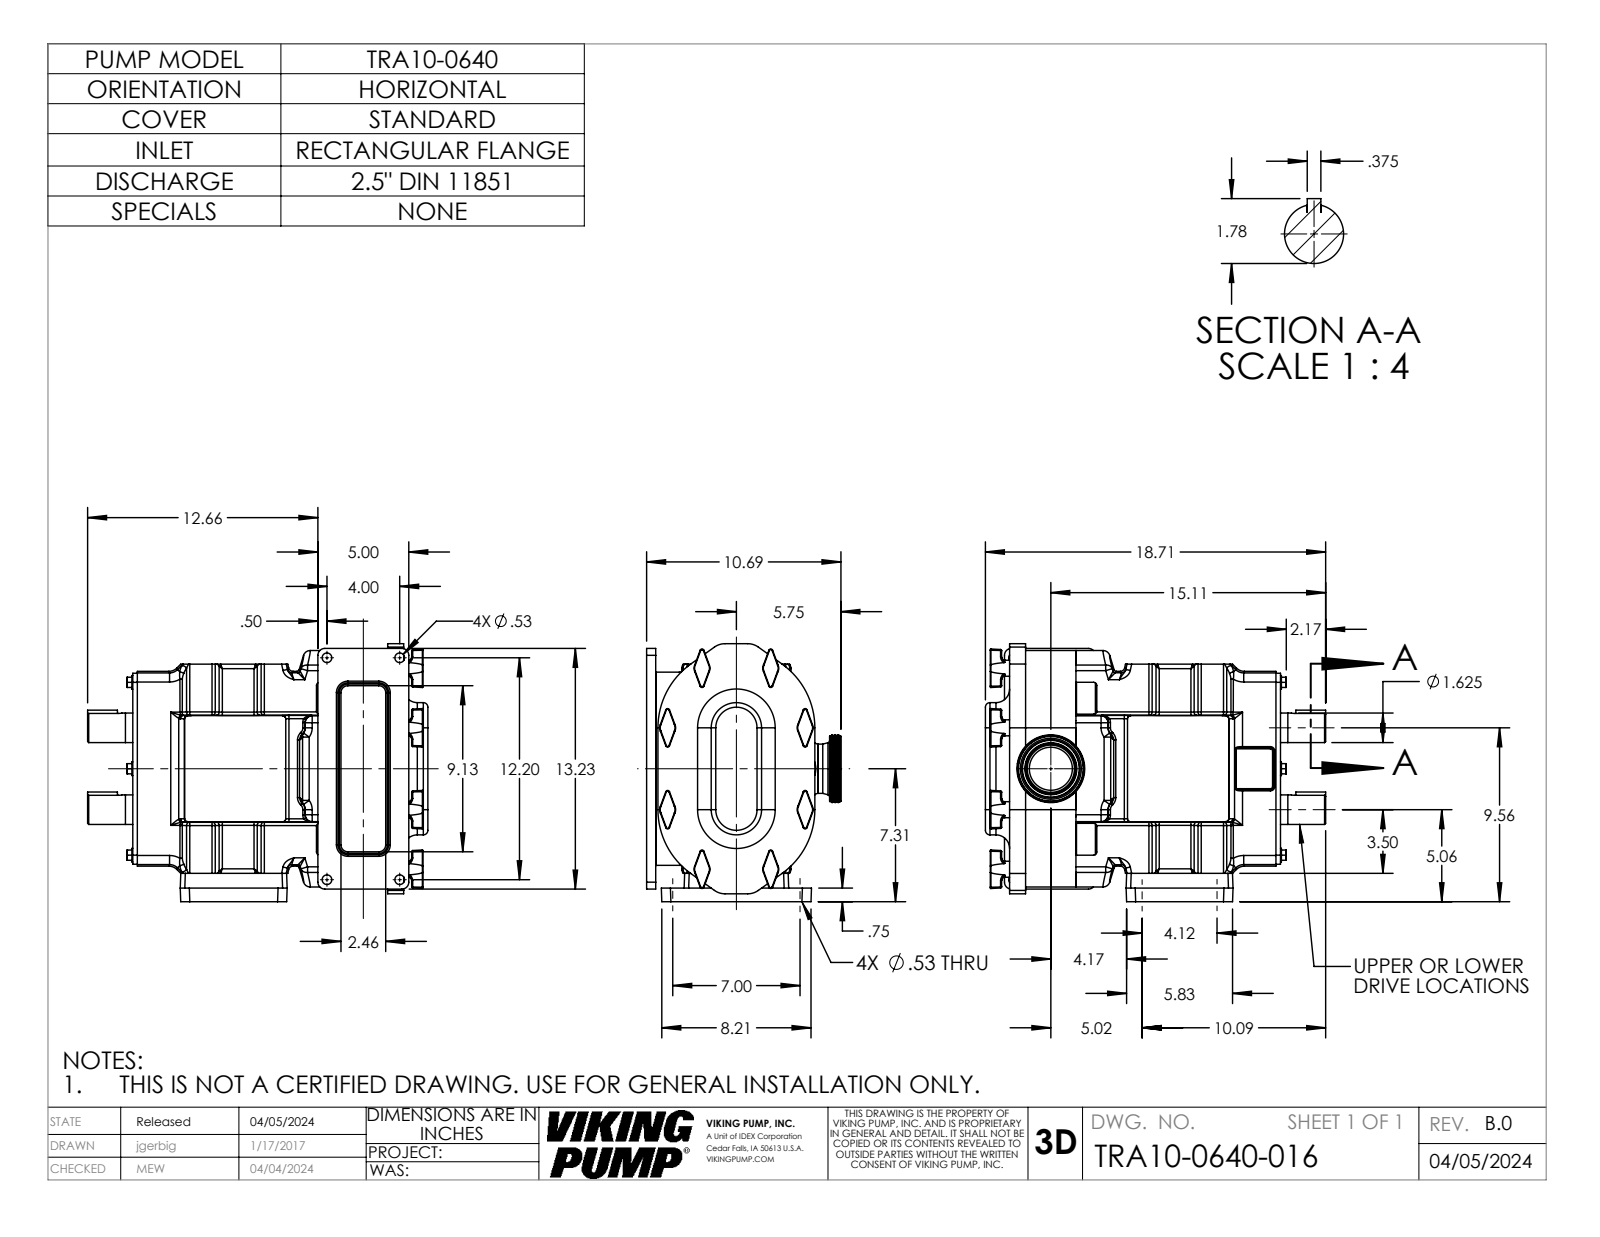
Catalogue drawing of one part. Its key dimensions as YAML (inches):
part_name: "TRA10-0640-BODY; TRA10-0640-016; 0600DIN11851-25; TRA10-0600-COVER-STD (+1 more)"
step_written_by: "SolidWorks 2022 (AUTOMOTIVE_DESIGN)"
units: inches
bodies: {solids: 4, faces: 1122, planar: 297, cylindrical: 395, other: 430}
overall_size: [18.714, 14.185, 10.688]
volume: 1230
surface_area: 1443
round_holes:
  - {diameter: 0.531, count: 8}
  - {diameter: 2.368, count: 1}
  - {diameter: 2.598, count: 1}
  - {diameter: 3.181, count: 1}
round_bosses_or_shafts:
  - {diameter: 0.88, count: 8}
  - {diameter: 0.75, count: 6}
  - {diameter: 1.624, count: 2}
  - {diameter: 2.795, count: 1}
  - {diameter: 2.708, count: 1}
partial_cylinders:
  - {radius: 0.18, count: 44}
  - {radius: 0.06, count: 43}
  - {radius: 0.03, count: 36}
  - {radius: 0.38, count: 36}
  - {radius: 0.25, count: 32}
  - {radius: 0.12, count: 24}
  - {radius: 0.5, count: 22}
  - {radius: 0.09, count: 16}
face_to_face_distances: [2.769, 0.5, 1.437, 0.88, 3.649, 7.937, 0.36, 11.25, 14.899, 14.019]
hole_center_spacings: [4, 4.12, 6.404, 6.435, 7, 8.122, 12.2, 12.839]
